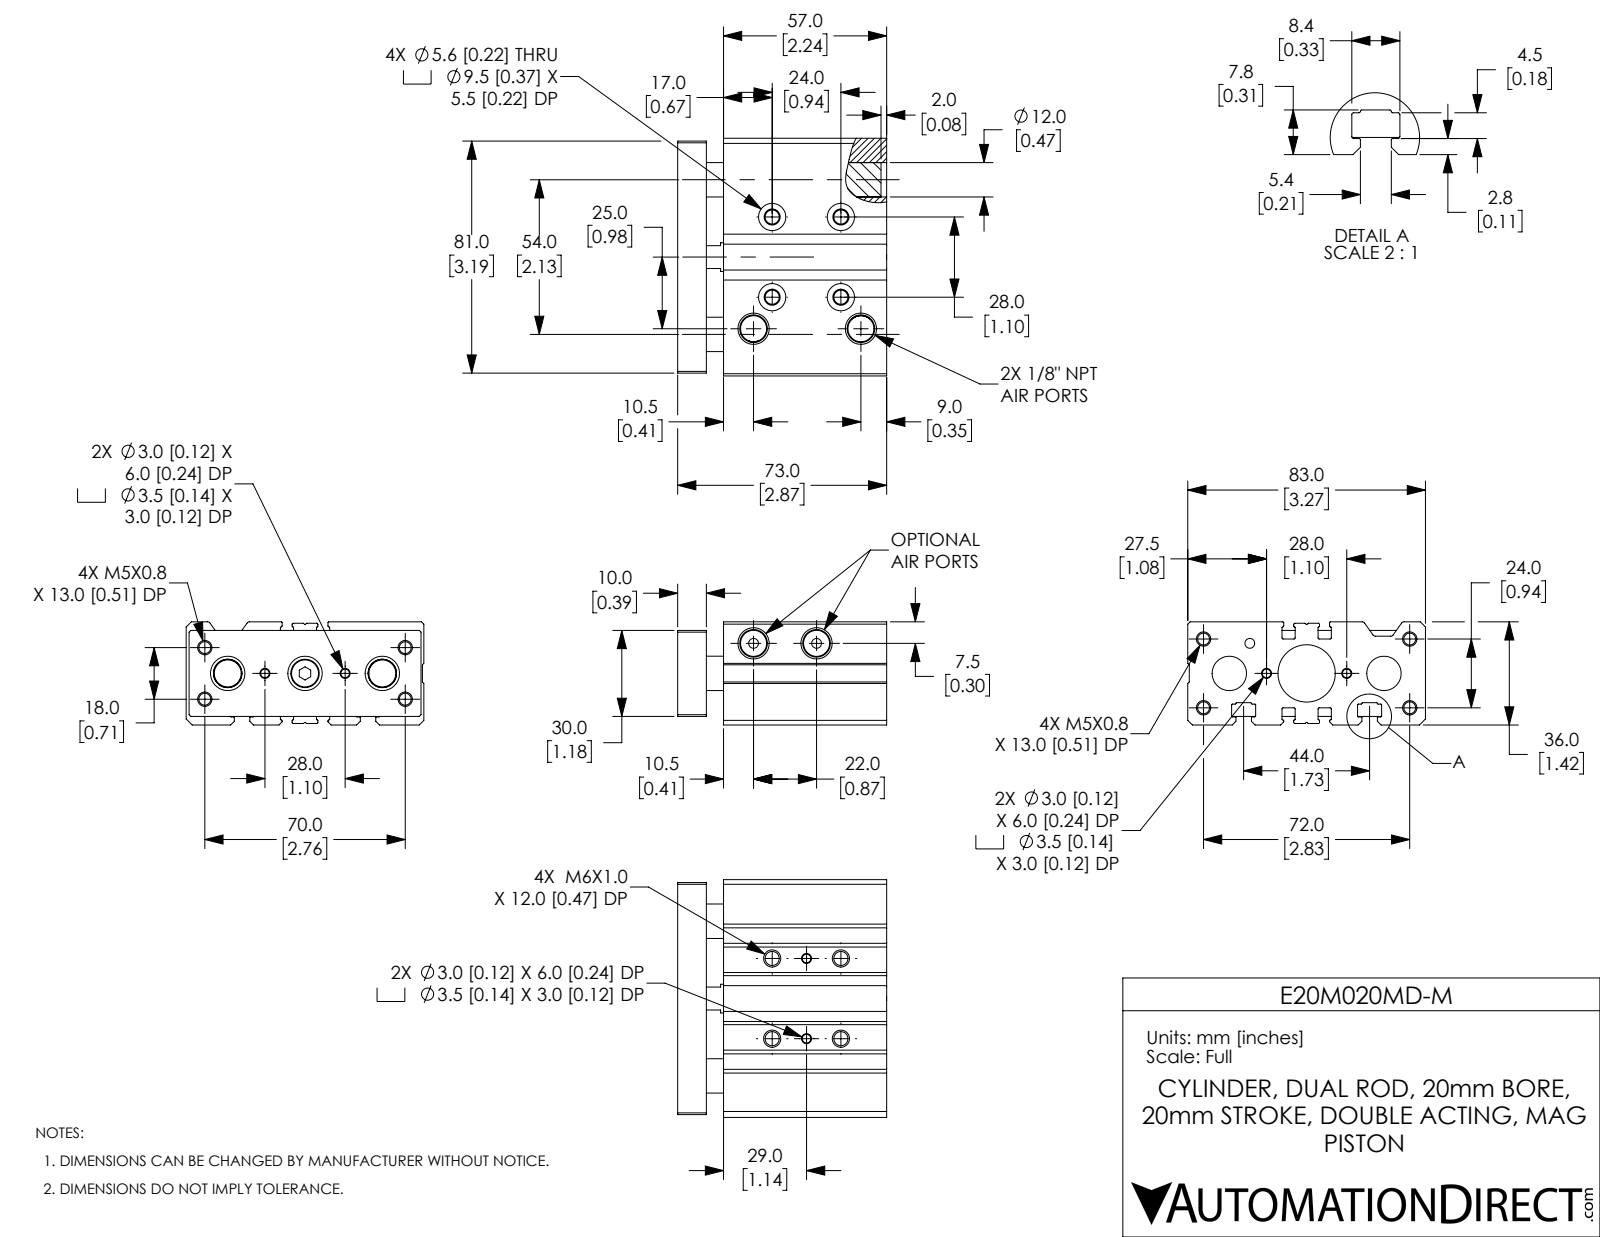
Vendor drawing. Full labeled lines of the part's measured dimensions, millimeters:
Part name (STEP PRODUCT): E20M020MD-M_ENDPLATE; E20M020MD-M_BODY; E20M020MD-M
STEP written by: SolidWorks 2019 (CONFIG_CONTROL_DESIGN)
Units: millimetres
Bodies: 5 solids, 404 faces (128 planar, 182 cylindrical, 94 other)
Overall size (bounding box): 83 × 73 × 36
Volume: 164 903 mm³ · Surface area: 54 301 mm²
Round holes (diameter × count): ⌀4.13 ×8, ⌀3 ×4, ⌀3.5 ×4, ⌀4.92 ×4, ⌀5.6 ×4, ⌀9.5 ×4, ⌀6 ×3, ⌀12 ×3, ⌀3.43 ×2, ⌀9.91 ×2, ⌀3.43 ×1, ⌀12 ×1
Round bosses / shafts (diameter × count): ⌀10 ×1, ⌀9.91 ×1
Partial cylindrical surfaces — rounded edges, fillets, slot ends (radius × count): R0.4 ×20, R0.2 ×18, R0.3 ×10, R0.25 ×8, R1 ×4
Main face-to-face distances: 6, 3, 36, 16, 63, 0.5, 73, 57, 10, 30
Hole centre spacings: 3.16, 12, 12.04, 15, 21.02, 22.85, 24, 25.06
